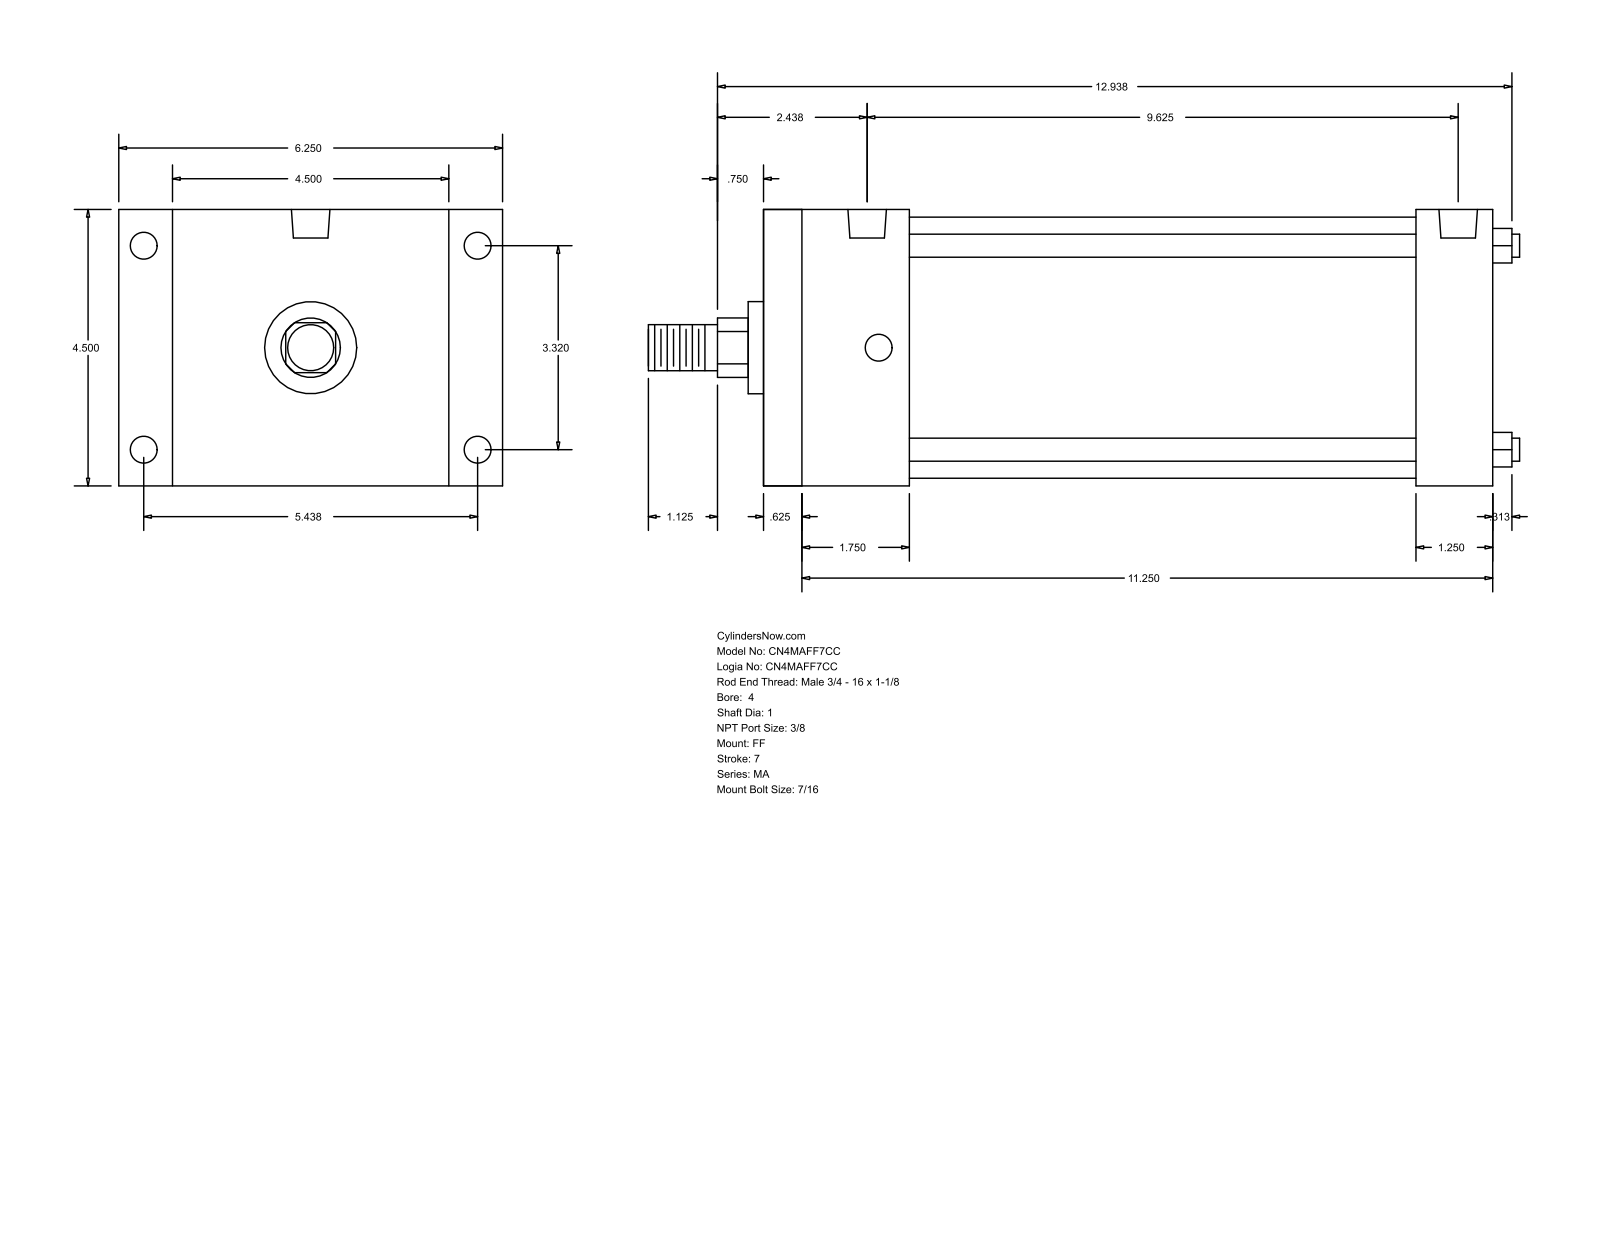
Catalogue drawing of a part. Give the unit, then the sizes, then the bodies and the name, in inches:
Units: inches
Overall size (bounding box): 14.187 × 6.25 × 4.5
Round holes (diameter × count): ⌀0.437 ×8, ⌀0.627 ×2
Round bosses / shafts (diameter × count): ⌀0.375 ×4, ⌀4.25 ×1, ⌀1.5 ×1, ⌀1 ×1, ⌀0.75 ×1
Partial cylindrical surfaces — rounded edges, fillets, slot ends (radius × count): R0.484 ×1
Main face-to-face distances: 4.5, 11.875, 0.625, 11.25, 0.875, 5.375, 10.625, 10, 1.25, 2.375
Hole centre spacings: 3.32, 5.438, 6.371, 9.25, 0.187, 0.188, 9.437, 9.438
Bodies: 0 solids, 92 faces (64 planar, 28 cylindrical, 0 other)
Part name (STEP PRODUCT): MA_FF__0400_1
STEP written by: GSSL Pune (CONFIG_CONTROL_DESIGN)
